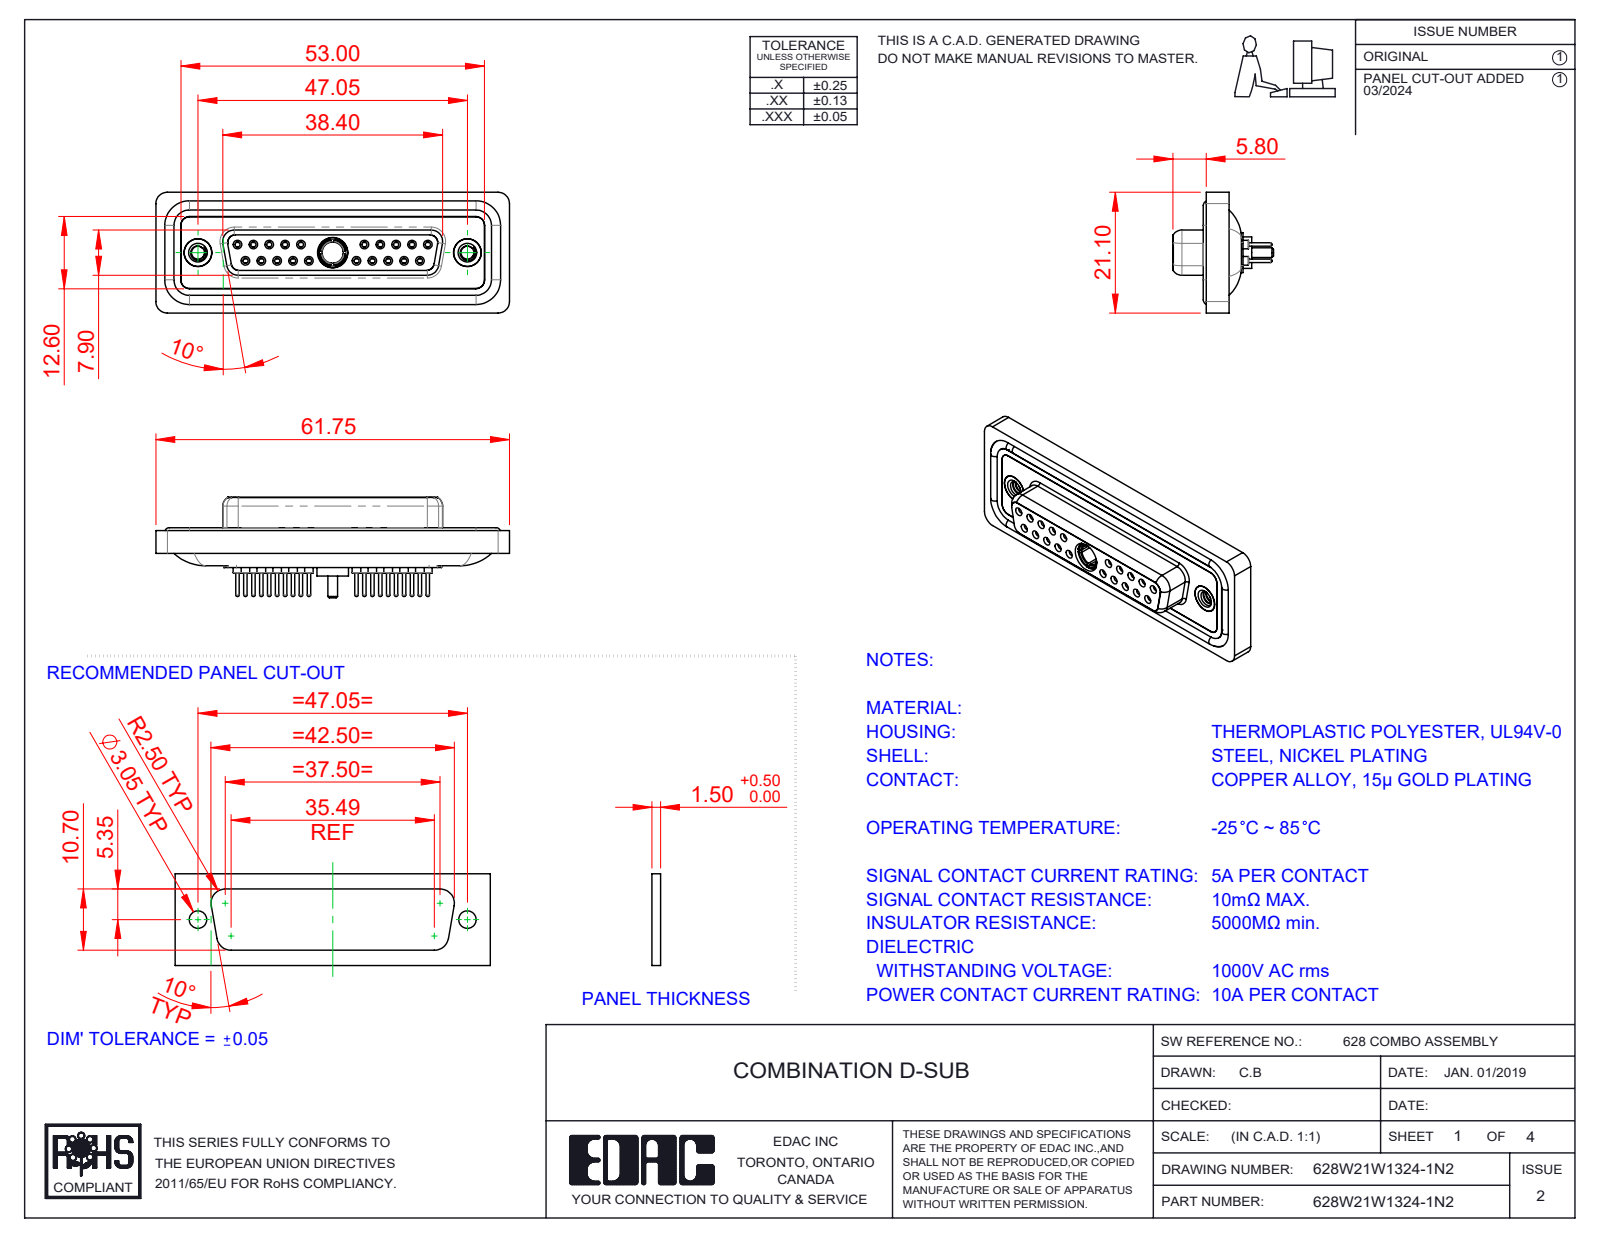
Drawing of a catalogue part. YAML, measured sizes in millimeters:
part_name: "628Combo Shell Front_25 Contacts; 628Combo Contact Row 1_24; Power Socket_10A S; 628Combo Shell Rear_25 Contacts (+5 more)"
step_written_by: "SolidWorks 2023 (CONFIG_CONTROL_DESIGN)"
units: millimeters
bodies: {solids: 29, faces: 1560, planar: 434, cylindrical: 591, other: 535}
overall_size: [61.75, 21.1, 17.55]
volume: 8359
surface_area: 13989
round_holes:
  - {diameter: 0.9, count: 20}
  - {diameter: 1.1, count: 20}
  - {diameter: 1.5, count: 20}
  - {diameter: 2, count: 20}
  - {diameter: 1.6, count: 10}
  - {diameter: 1.7, count: 10}
  - {diameter: 4.85, count: 3}
  - {diameter: 2.26, count: 2}
  - {diameter: 4, count: 2}
  - {diameter: 4.05, count: 2}
  - {diameter: 5, count: 2}
  - {diameter: 3.7, count: 1}
round_bosses_or_shafts:
  - {diameter: 2.2, count: 20}
  - {diameter: 0.6, count: 20}
  - {diameter: 1.6, count: 14}
  - {diameter: 4.95, count: 2}
  - {diameter: 4.8, count: 2}
  - {diameter: 5.5, count: 1}
  - {diameter: 5.2, count: 1}
  - {diameter: 4.96, count: 1}
partial_cylinders:
  - {radius: 1.5, count: 22}
  - {radius: 2, count: 18}
  - {radius: 1.35, count: 8}
  - {radius: 1.6, count: 8}
  - {radius: 0.25, count: 4}
  - {radius: 0.5, count: 4}
  - {radius: 0.6, count: 4}
  - {radius: 0.65, count: 4}
face_to_face_distances: [0.4, 1.8, 7.45, 6.6, 5.65, 0.5, 1.6, 7.05, 2.9, 1.1]
hole_center_spacings: [3.16, 2.77, 5.54, 5.03, 8.31, 7.48, 16.62, 19.39]
